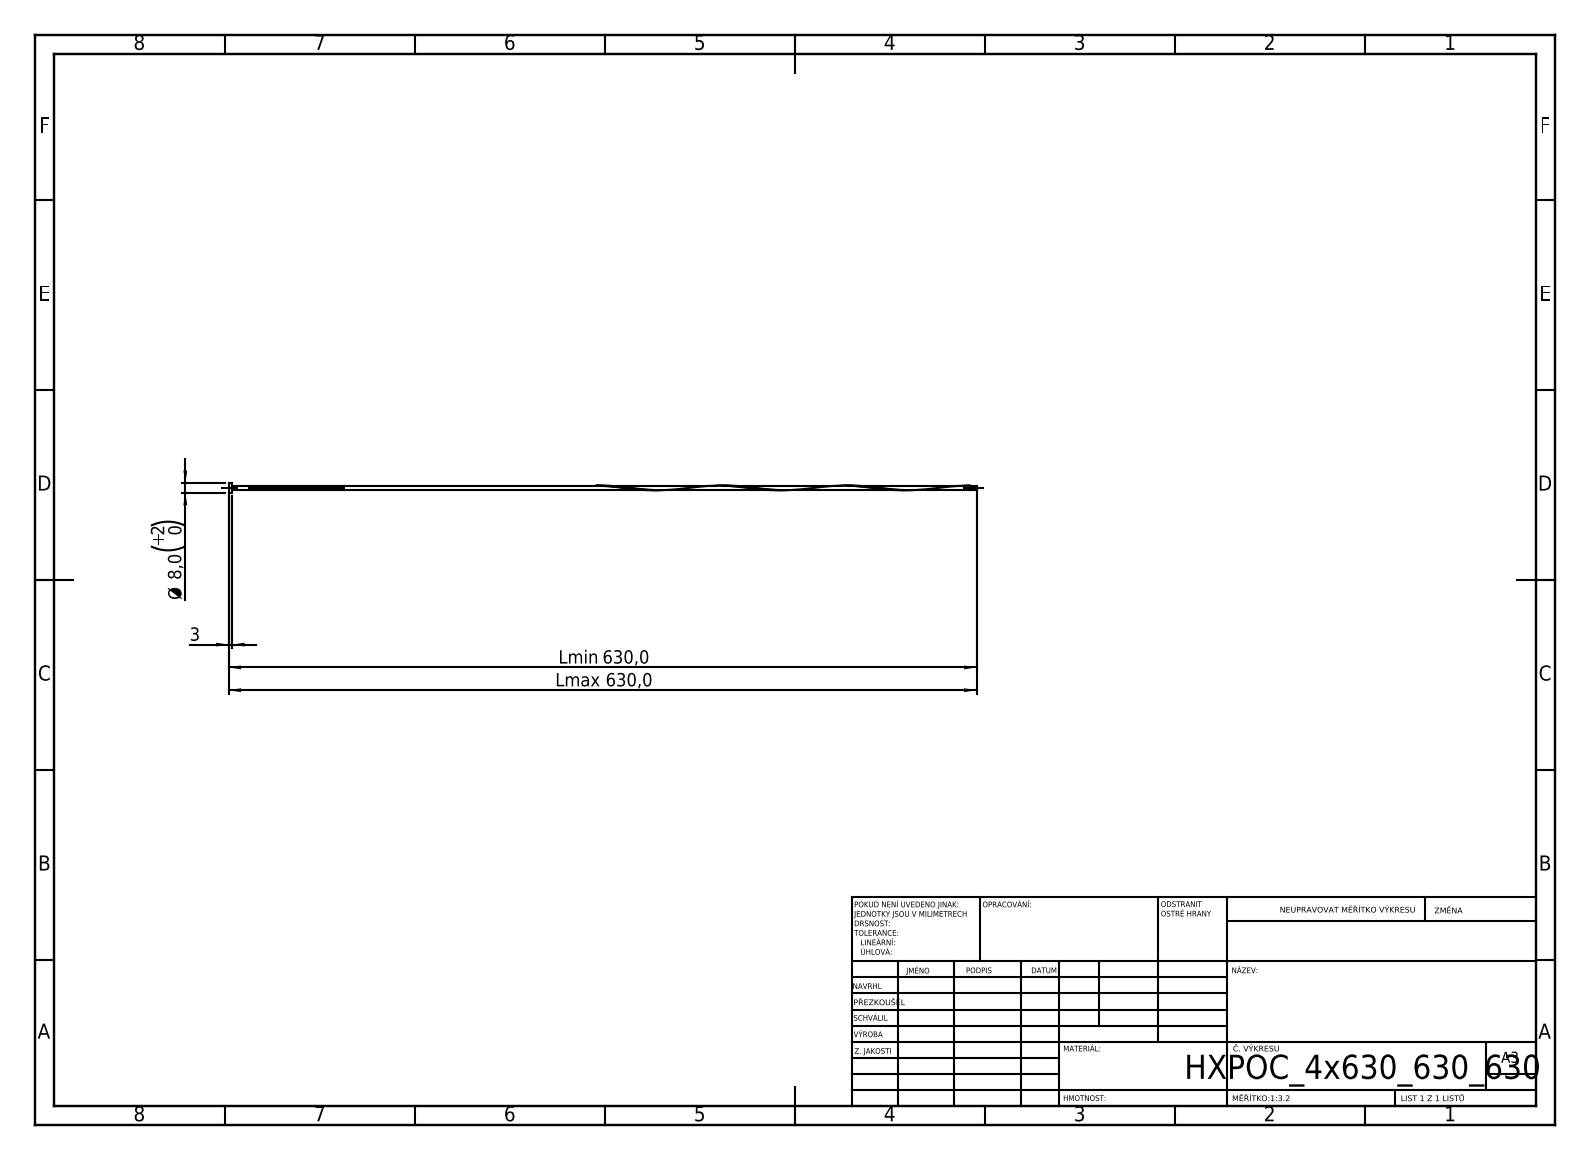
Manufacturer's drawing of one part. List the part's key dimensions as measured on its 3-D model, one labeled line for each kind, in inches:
STEP written by: SolidWorks 2019 (CONFIG_CONTROL_DESIGN)
Units: inches
Bodies: 1 solid, 16 faces (6 planar, 9 cylindrical, 1 other)
Overall size (bounding box): 24.803 × 0.315 × 0.315
Volume: 0.593 in³ · Surface area: 16.77 in²
Round bosses / shafts (diameter × count): ⌀0.315 ×1, ⌀0.157 ×1, ⌀0.126 ×1
Main face-to-face distances: 0.118, 24.803, 24.685, 24.606, 24.488, 0.197, 24.574, 24.456, 0.031, 0.229
